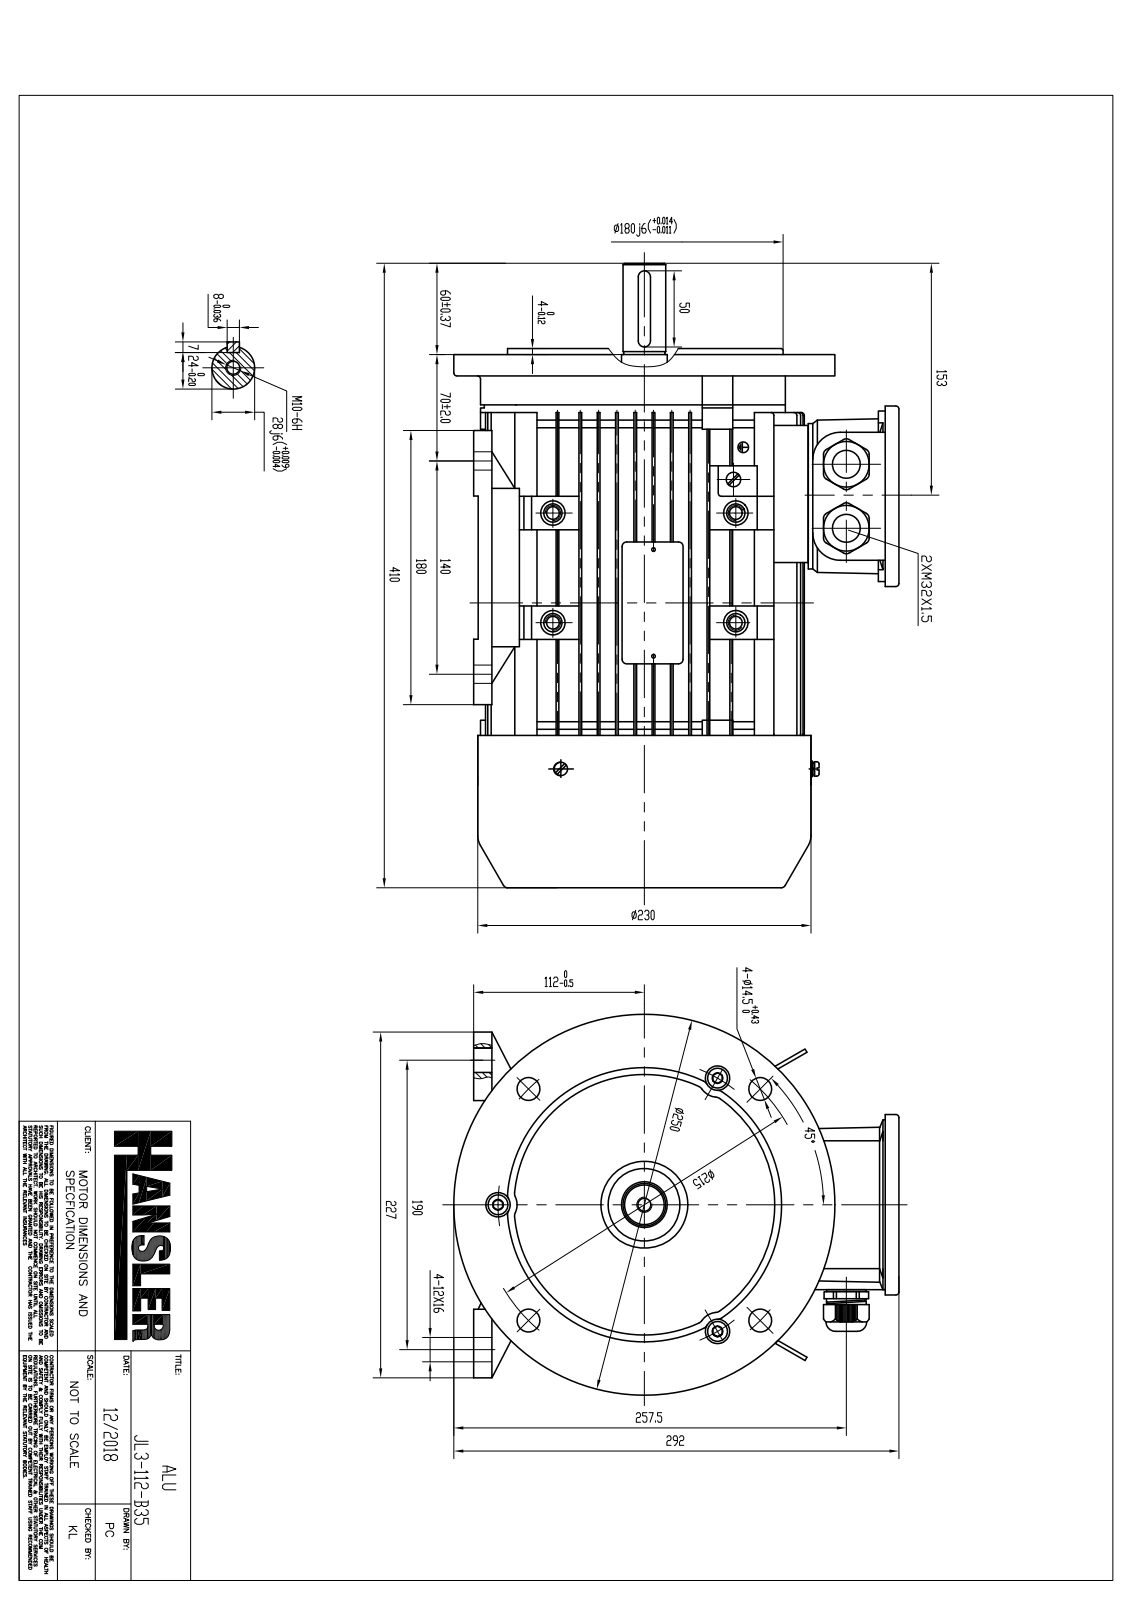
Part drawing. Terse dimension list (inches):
name: JL3-112-B35
written by: SolidWorks 2018 (CONFIG_CONTROL_DESIGN)
unit: in
bodies: 56 solids, 4191 faces (1929 planar, 1766 cylindrical, 496 other)
size: 15.551 × 11.876 × 9.843
volume: 183.7 in³; area: 2 041 in²
holes: 12× ⌀0.315, 10× ⌀0.228, 8× ⌀0.709, 7× ⌀0.63, 6× ⌀0.197, 6× ⌀0.433, 4× ⌀0.157, 4× ⌀0.207, 4× ⌀0.209, 4× ⌀0.394, 4× ⌀0.415, 4× ⌀0.512
bosses: 8× ⌀0.472, 8× ⌀0.394, 8× ⌀0.197, 4× ⌀0.669, 4× ⌀0.63, 4× ⌀0.62, 4× ⌀0.374, 4× ⌀0.309
rounds: 656× R0.02, 72× R0.039, 47× R0.118, 33× R0.197, 32× R0.079, 20× R0.157, 16× R0.012, 14× R0.236
face distances: 0.071, 0.591, 0.551, 3.937, 3.346, 0.661, 2.795, 4.528, 1.142, 2.205
hole spacings: 3.32, 3.858, 0.837, 1.727, 0.056, 0.709, 0.817, 0.835
